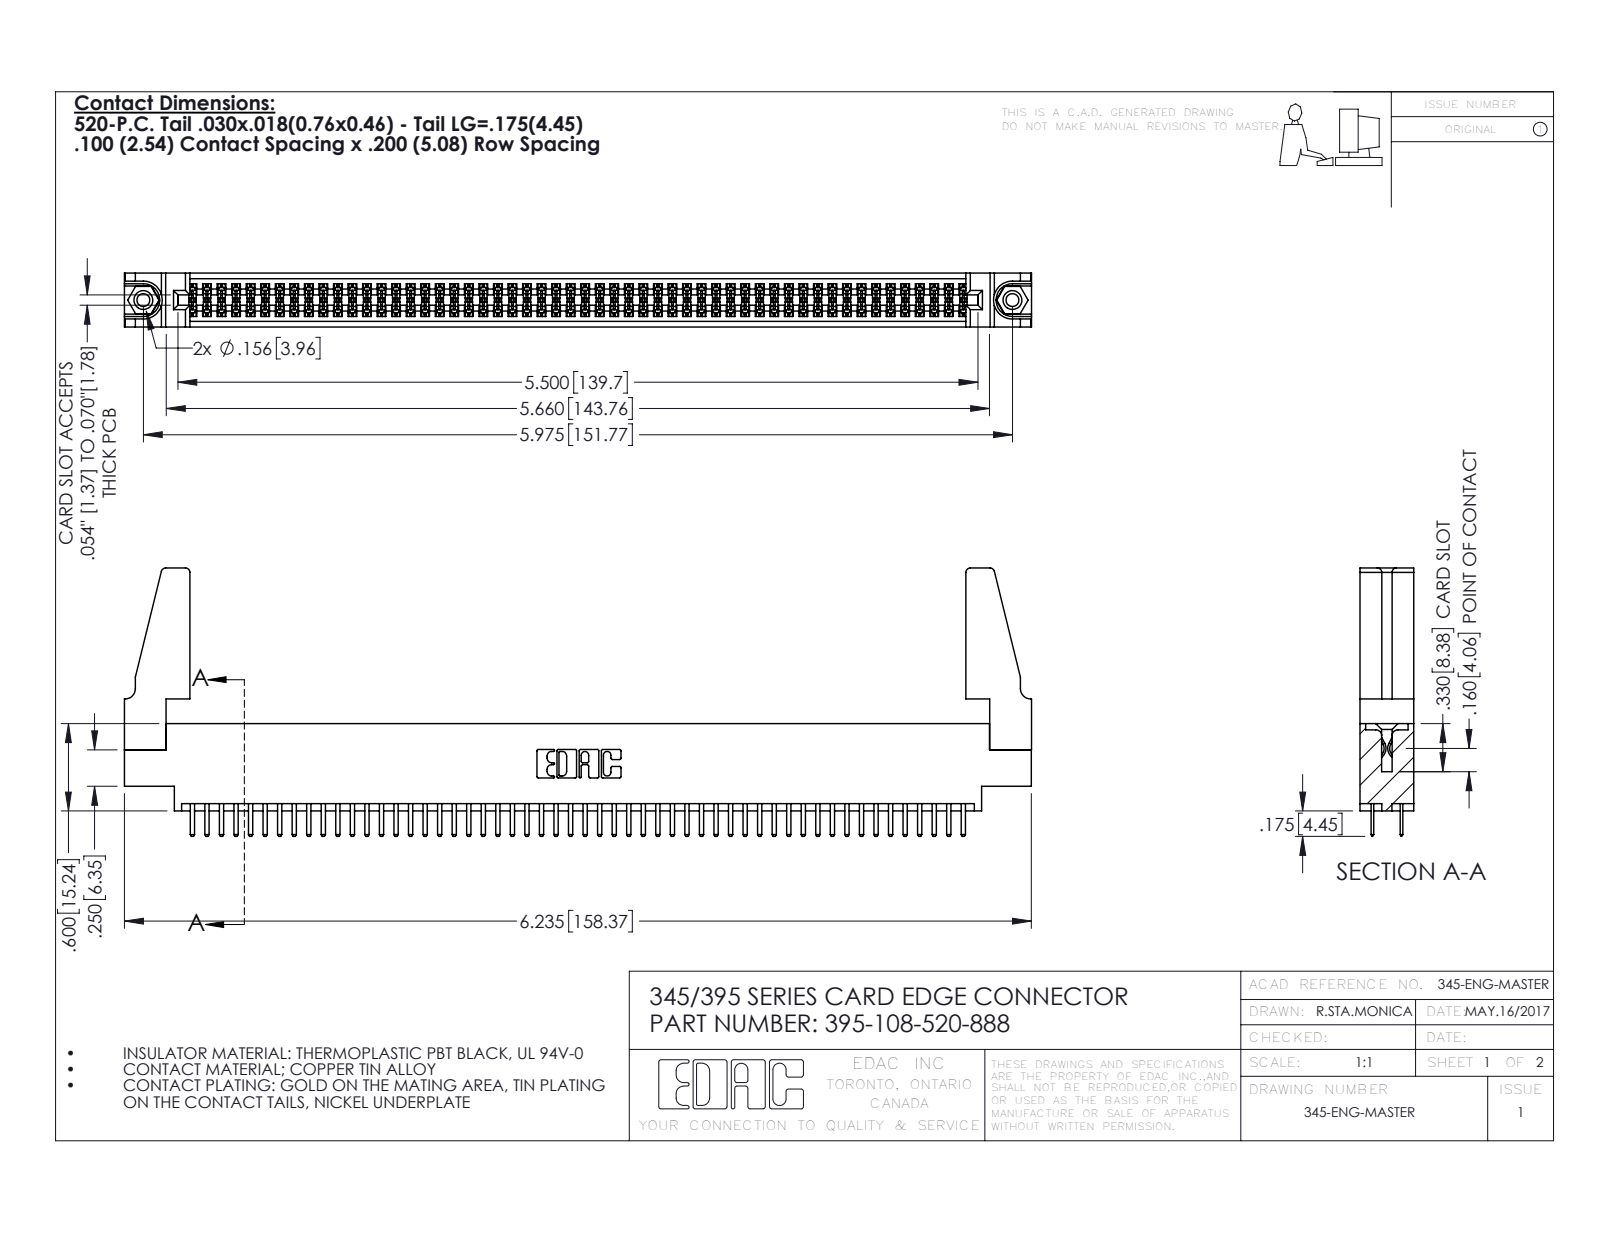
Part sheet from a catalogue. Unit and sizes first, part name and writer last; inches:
Units: inches
Overall size (bounding box): 6.236 × 1.845 × 0.37
Round holes (diameter × count): ⌀0.089 ×2, ⌀0.125 ×2, ⌀0.156 ×2, ⌀0.064 ×1
Round bosses / shafts (diameter × count): ⌀0.155 ×2
Partial cylindrical surfaces — rounded edges, fillets, slot ends (radius × count): R0.006 ×162, R0.01 ×112, R0.01 ×22, R0.03 ×8, R0.007 ×6, R0.031 ×6, R0.026 ×3, R0.014 ×2
Main face-to-face distances: 0.072, 0.298, 0.37, 0.2, 0.098, 0.272, 0.025, 0.225, 0.022, 0.072
Hole centre spacings: 0.27, 5.739, 5.975
Volume: 1.134 in³ · Surface area: 40.41 in²
Bodies: 113 solids, 6086 faces (3936 planar, 2134 cylindrical, 16 other)
Part name (STEP PRODUCT): 345-292-001_345-293-120; 345 Part_0.170 Offset - 0.156 Dia-TH; 345-250-001_345-250-001-102; 395-108-520-888 (+1 more)
STEP written by: SolidWorks 2016 (CONFIG_CONTROL_DESIGN)
